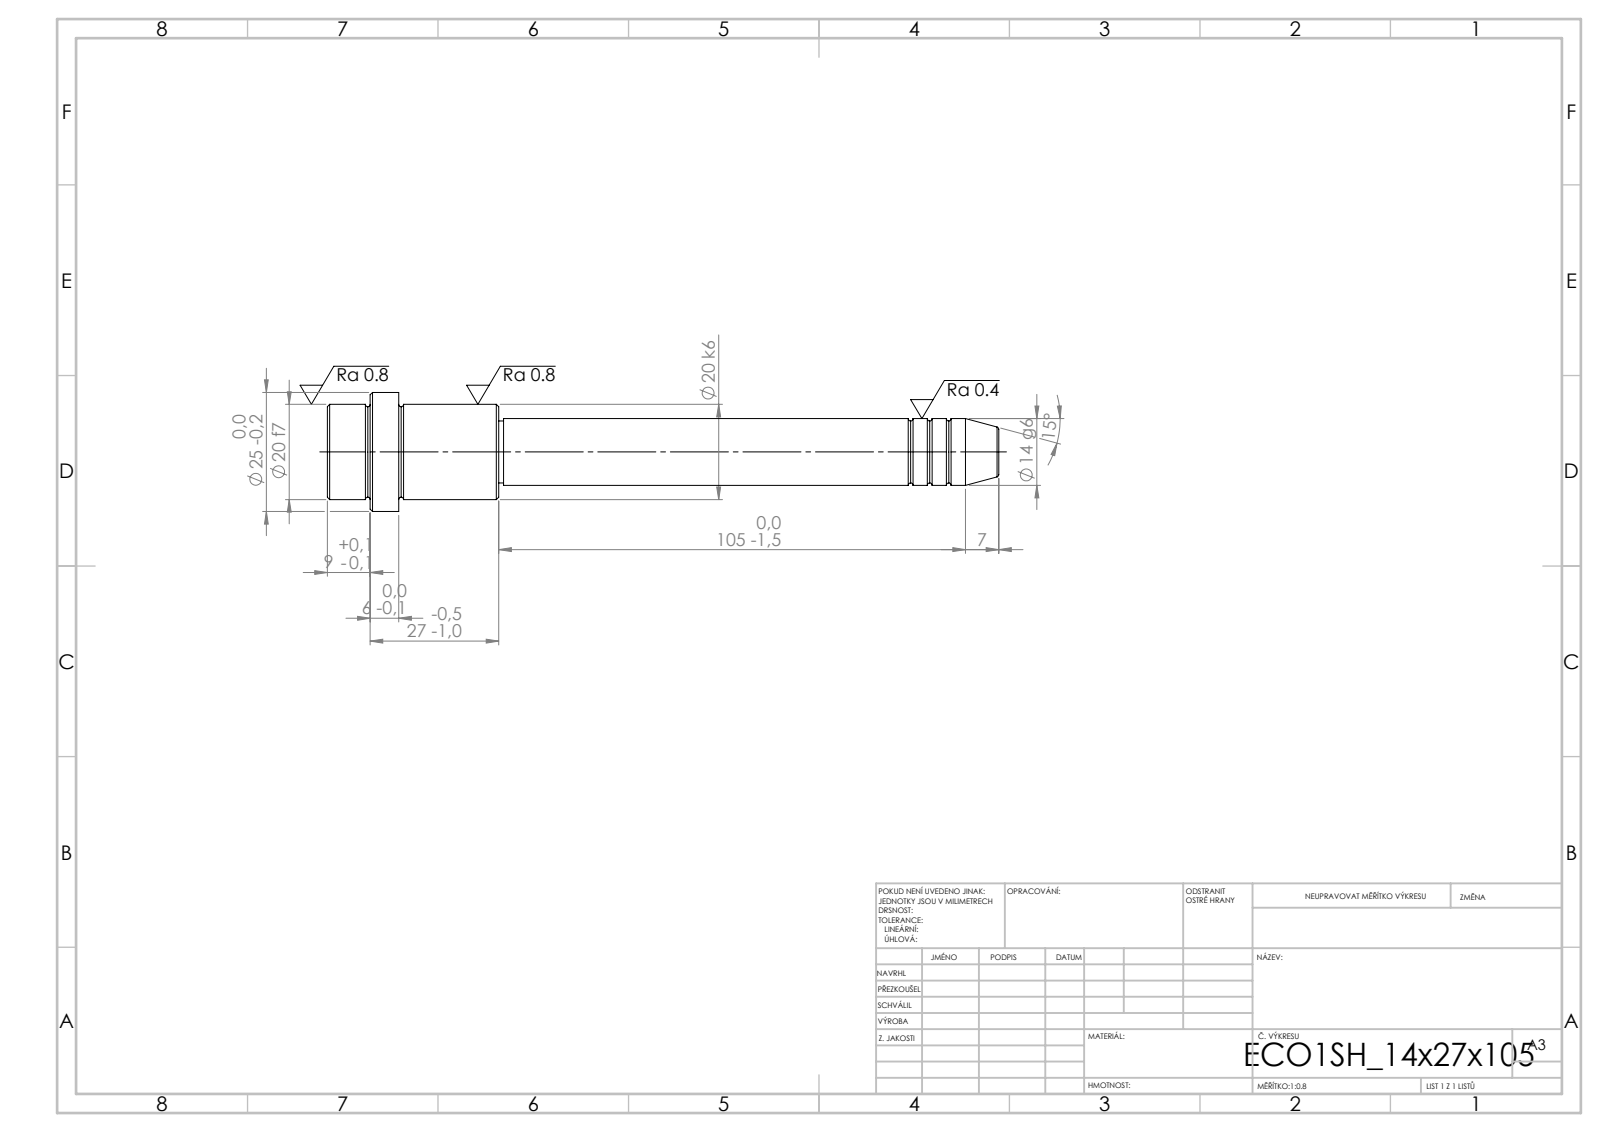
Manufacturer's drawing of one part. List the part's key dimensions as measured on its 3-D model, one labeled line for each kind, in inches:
STEP written by: SolidWorks 2019 (CONFIG_CONTROL_DESIGN)
Units: inches
Bodies: 1 solid, 52 faces (6 planar, 16 cylindrical, 30 other)
Overall size (bounding box): 5.551 × 0.984 × 0.984
Volume: 1.716 in³ · Surface area: 12.34 in²
Round bosses / shafts (diameter × count): ⌀0.984 ×1, ⌀0.787 ×1, ⌀0.551 ×1, ⌀0.512 ×1
Main face-to-face distances: 0.591, 0.827, 1.417, 1.063, 0.236, 0.354, 4.134, 4.961, 5.197, 5.551
